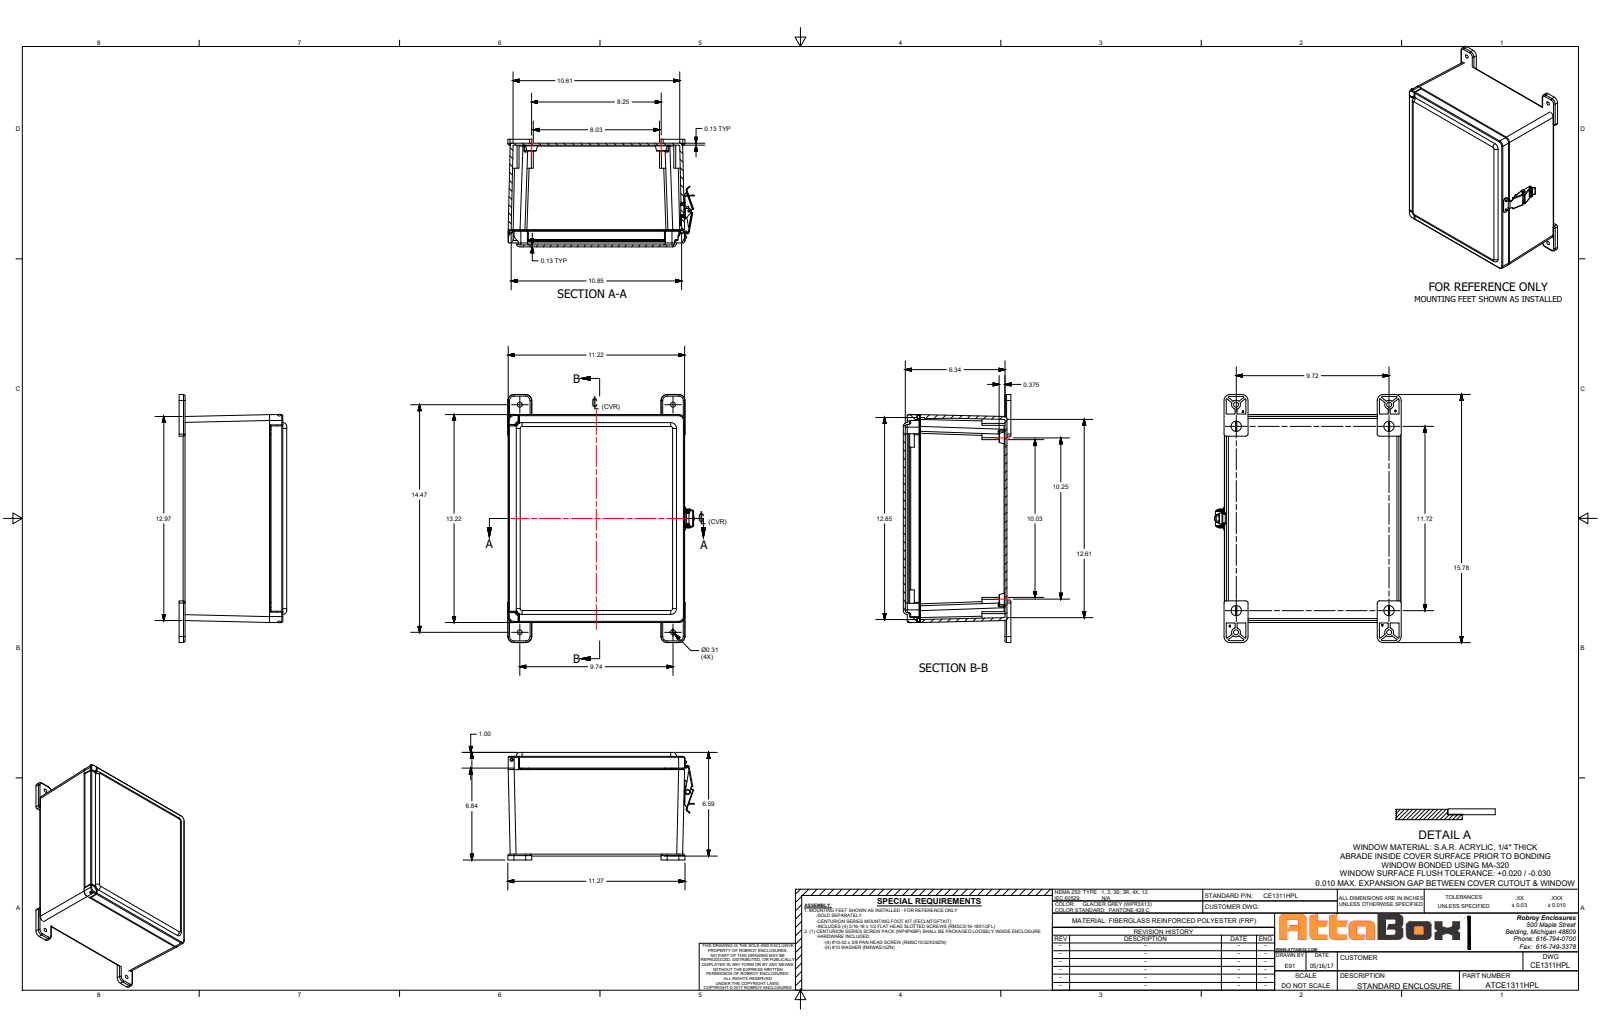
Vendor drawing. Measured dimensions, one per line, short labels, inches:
name: CE1311HPL
written by: SolidWorks 2018 (AUTOMOTIVE_DESIGN)
unit: in
bodies: 36 solids, 1589 faces (691 planar, 495 cylindrical, 403 other)
size: 15.781 × 11.867 × 6.844
volume: 114.1 in³; area: 1 364 in²
holes: 6× ⌀0.159, 6× ⌀0.281, 4× ⌀0.104, 4× ⌀0.14, 4× ⌀0.156, 4× ⌀0.313, 4× ⌀0.313, 4× ⌀0.344, 4× ⌀0.531, 2× ⌀0.096, 2× ⌀0.13, 2× ⌀0.13
bosses: 6× ⌀0.27, 5× ⌀0.125, 4× ⌀0.229, 2× ⌀0.375, 1× ⌀0.325, 1× ⌀0.3, 1× ⌀0.299, 1× ⌀0.185
rounds: 60× R0.031, 56× R0.031, 40× R0.125, 26× R0.062, 16× R0.25, 13× R0.1, 10× R0.375, 8× R0.045
face distances: 0.125, 6.469, 0.186, 6.594, 6.344, 0.125, 0.25, 6.344, 6.219, 0.75
hole spacings: 1.046, 11.447, 12.131, 13.506, 12.531, 0.574, 1.039, 1.375
